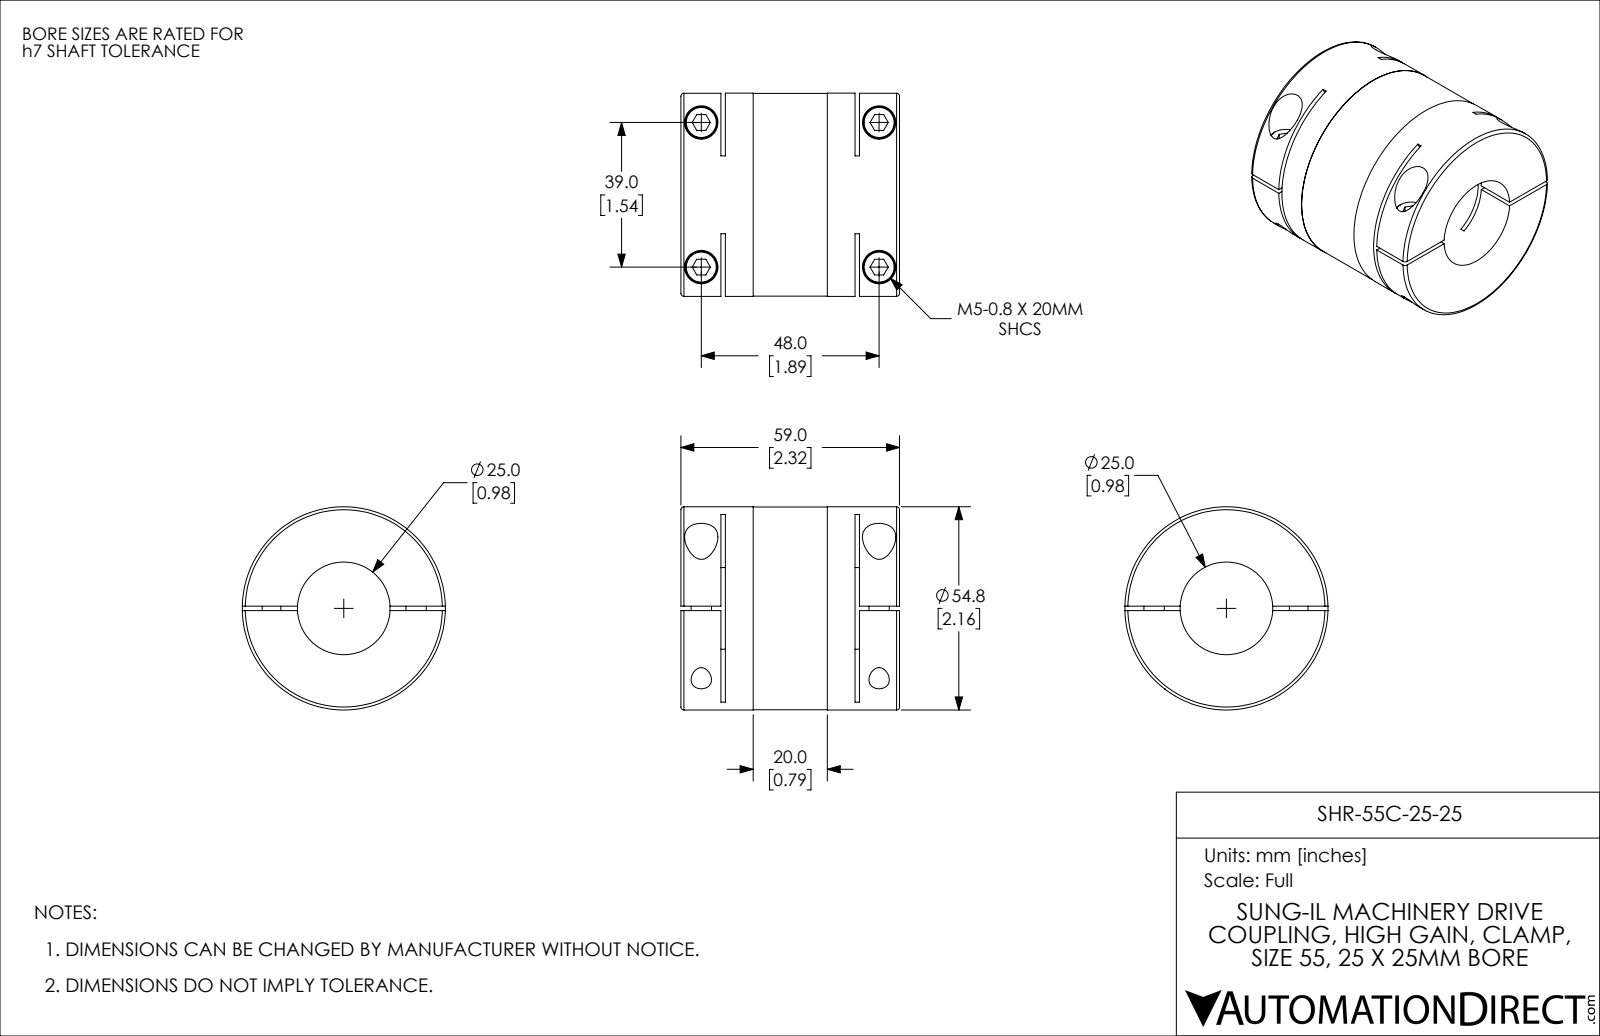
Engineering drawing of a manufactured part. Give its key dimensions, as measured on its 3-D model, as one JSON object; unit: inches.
{"part_name": "SHR-55C-25-25", "step_written_by": "SolidWorks 2021 (CONFIG_CONTROL_DESIGN)", "units": "inches", "bodies": {"solids": 1, "faces": 144, "planar": 70, "cylindrical": 58, "other": 16}, "overall_size": [2.323, 2.157, 2.157], "volume_in3": 6.197, "surface_area_in2": 43.95, "round_holes": [[0.217, 4], [0.354, 4], [0.984, 1], [1.063, 1]], "round_bosses_or_shafts": [[0.335, 4], [0.197, 2], [2.157, 1], [2.154, 1]], "partial_cylinders_radius": [[2.362, 2]], "face_to_face_distances": [0.047, 0.472, 1.85, 0.425, 1.898, 1.425, 2.323, 1.378, 1.472, 0.768], "hole_center_spacings": [1.535, 1.89, 2.435]}
